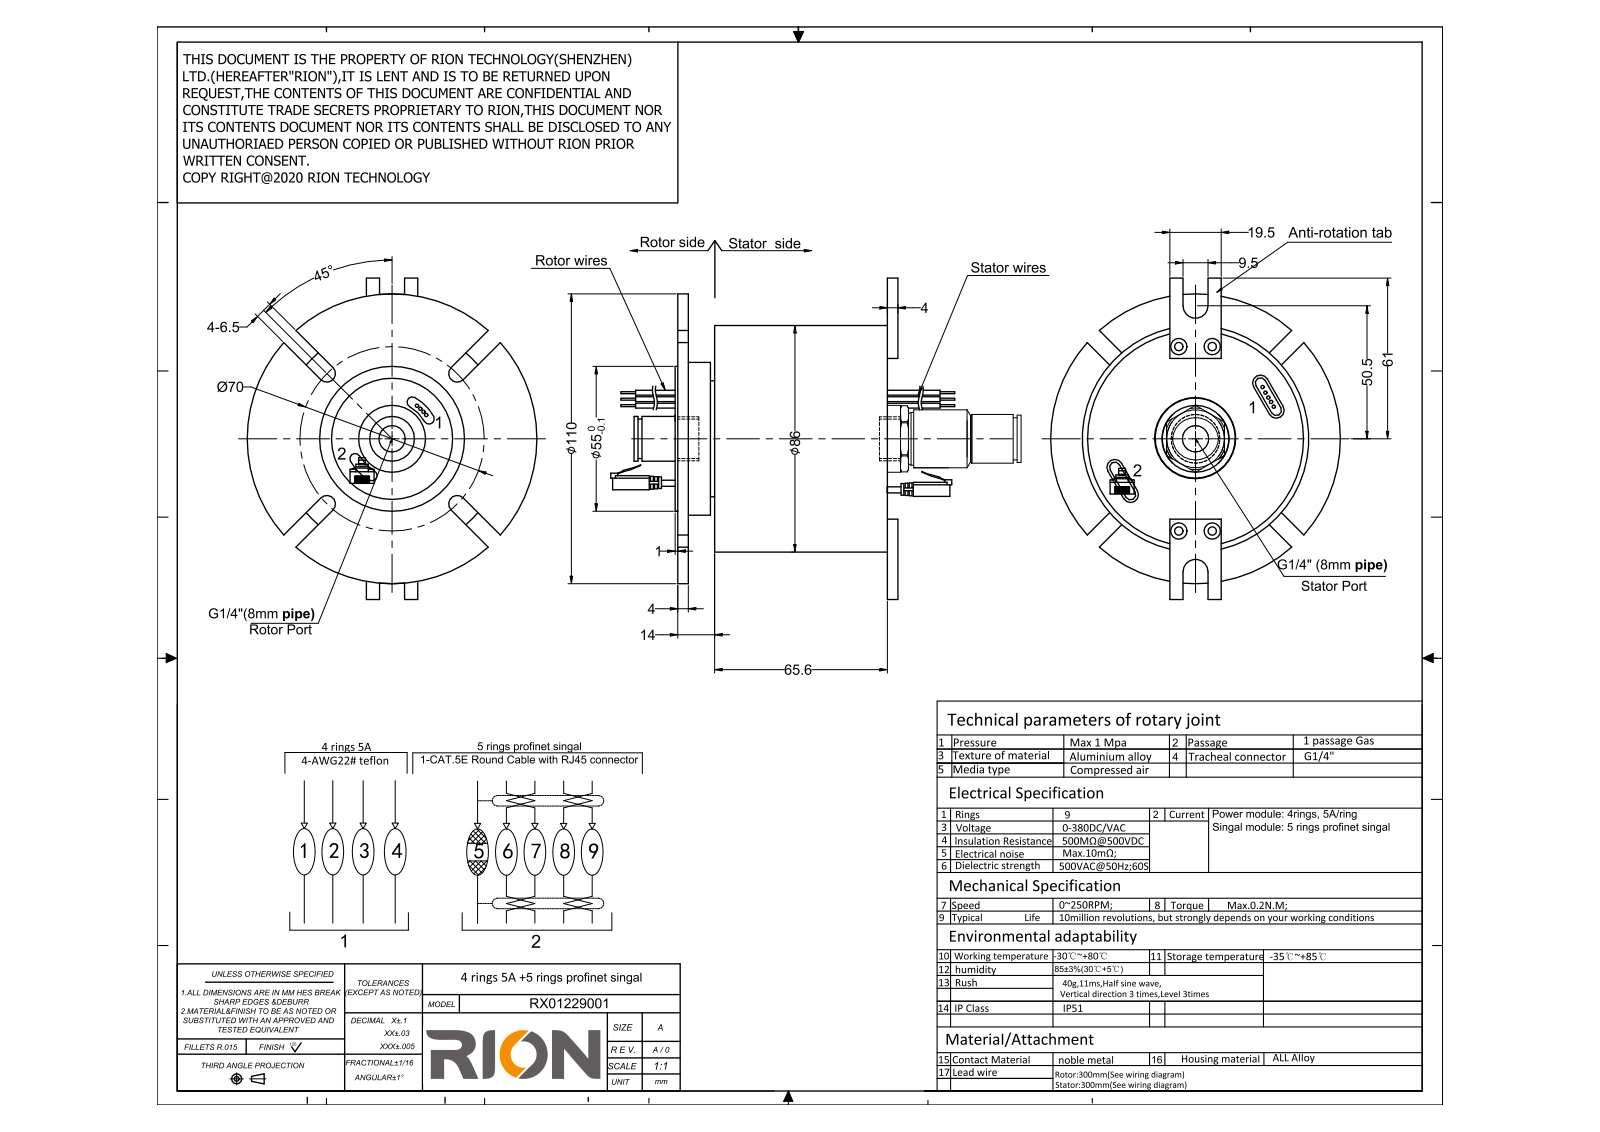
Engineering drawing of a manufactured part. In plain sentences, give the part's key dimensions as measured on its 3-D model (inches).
The part is named "KQ2S08-02S; KSH08-02S". Its 3-D file was written by "SolidWorks 2014 (CONFIG_CONTROL_DESIGN)". It is 3 solids with 269 faces: 98 planar, 131 cylindrical and 40 other. Overall it measures 5.224 by 4.803 by 4.331 inches. Its volume is 26.86 cubic inches and its surface area 108.4 square inches. Round holes: 4 of diameter 0.098, 4 of diameter 0.126, 1 of diameter 0.236, 1 of diameter 0.354, 1 of diameter 0.394, 1 of diameter 0.465, 1 of diameter 1, 1 of diameter 1.213, 1 of diameter 1.811, 1 of diameter 3.228. Round bosses or shafts: 8 of diameter 0.051, 2 of diameter 0.256, 1 of diameter 4.331, 1 of diameter 3.386, 1 of diameter 3.22, 1 of diameter 2.283, 1 of diameter 2.165, 1 of diameter 1.732. Partial cylindrical surfaces (rounded edges, fillets, slot ends): 8 of radius 0.079, 4 of radius 0.128, 2 of radius 0.187, 1 of radius 0.551, 1 of radius 0.709. The main face-to-face distances are 0.157, 3.134, 2.976, 0.551, 0.394, 2.583, 0.213, 0.055, 0.339, 2.921. The hole center spacings are 1.4, 0.5, 2.756, 2.801.
